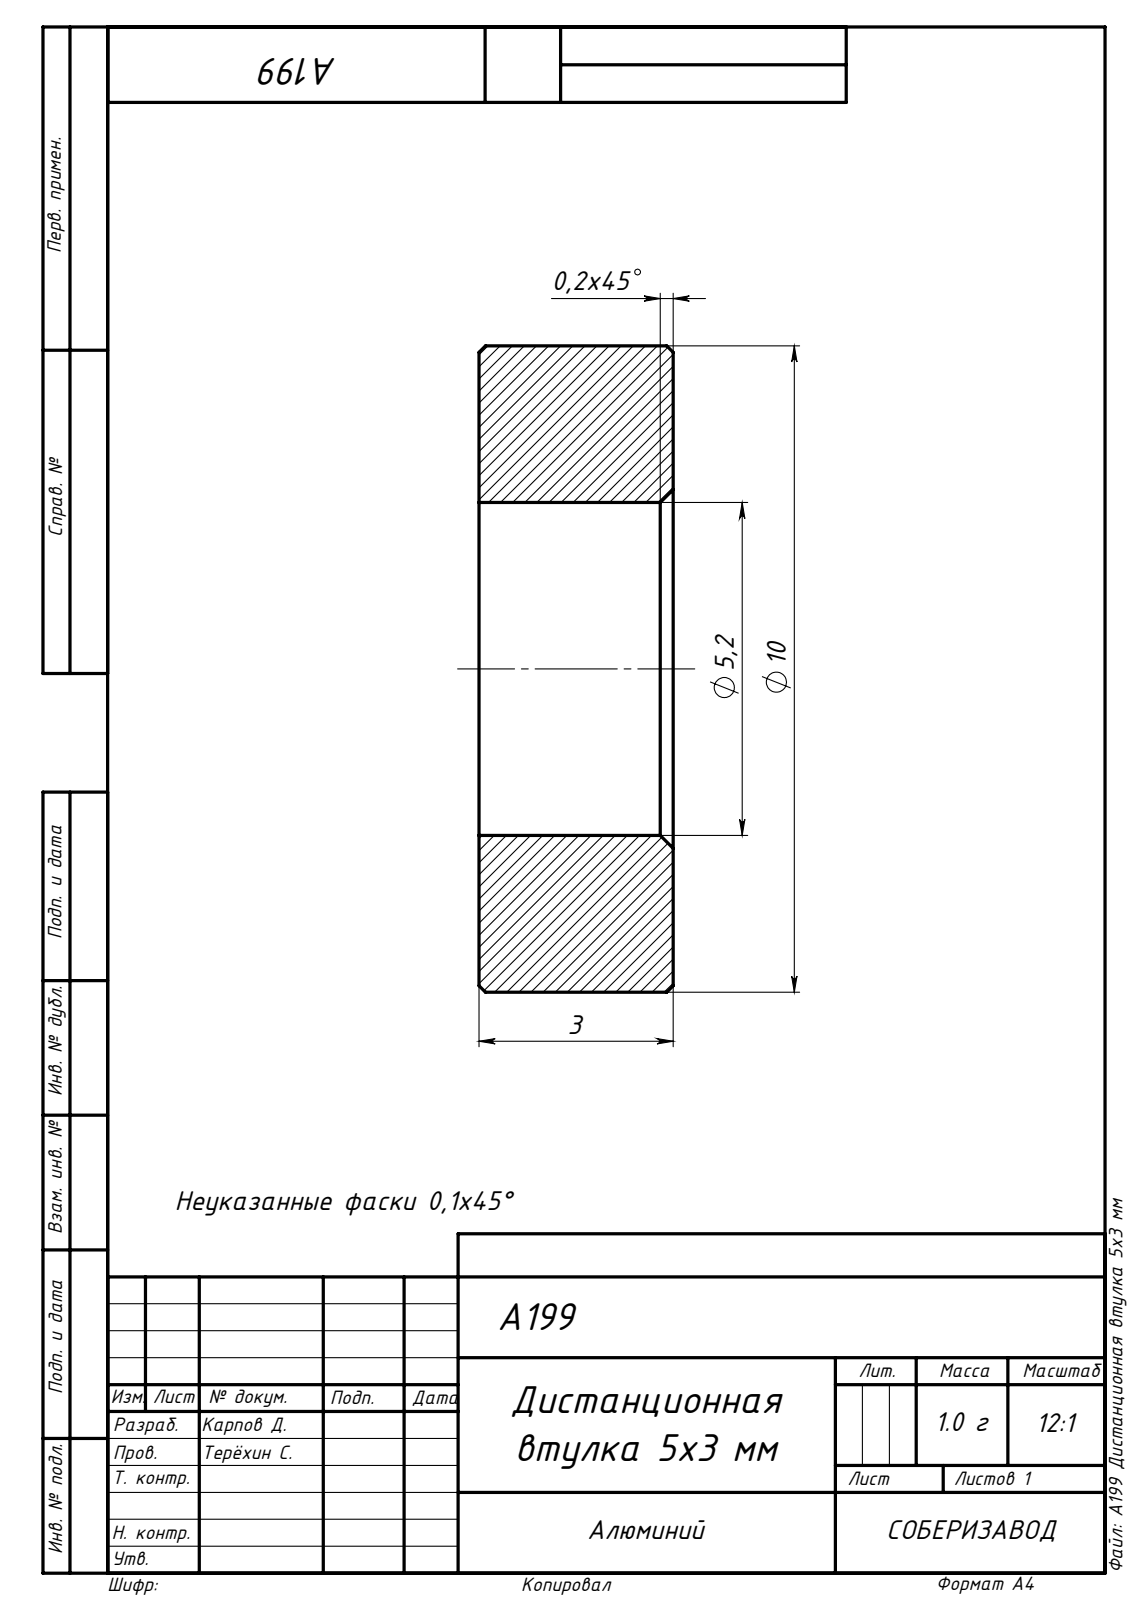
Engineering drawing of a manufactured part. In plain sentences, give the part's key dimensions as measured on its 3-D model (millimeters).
The part is named "A199 Дистанционная втулка 5х3 мм". Its 3-D file was written by "SolidWorks 2020 (AUTOMOTIVE_DESIGN)". It is 1 solid with 12 faces: 2 planar, 4 cylindrical and 6 other. Overall it measures 10 by 10 by 3 millimeters. Its volume is 172 cubic millimeters and its surface area 253 square millimeters. Round holes: 1 of diameter 5.15. Round bosses or shafts: 1 of diameter 10. The main face-to-face distances are 3.
